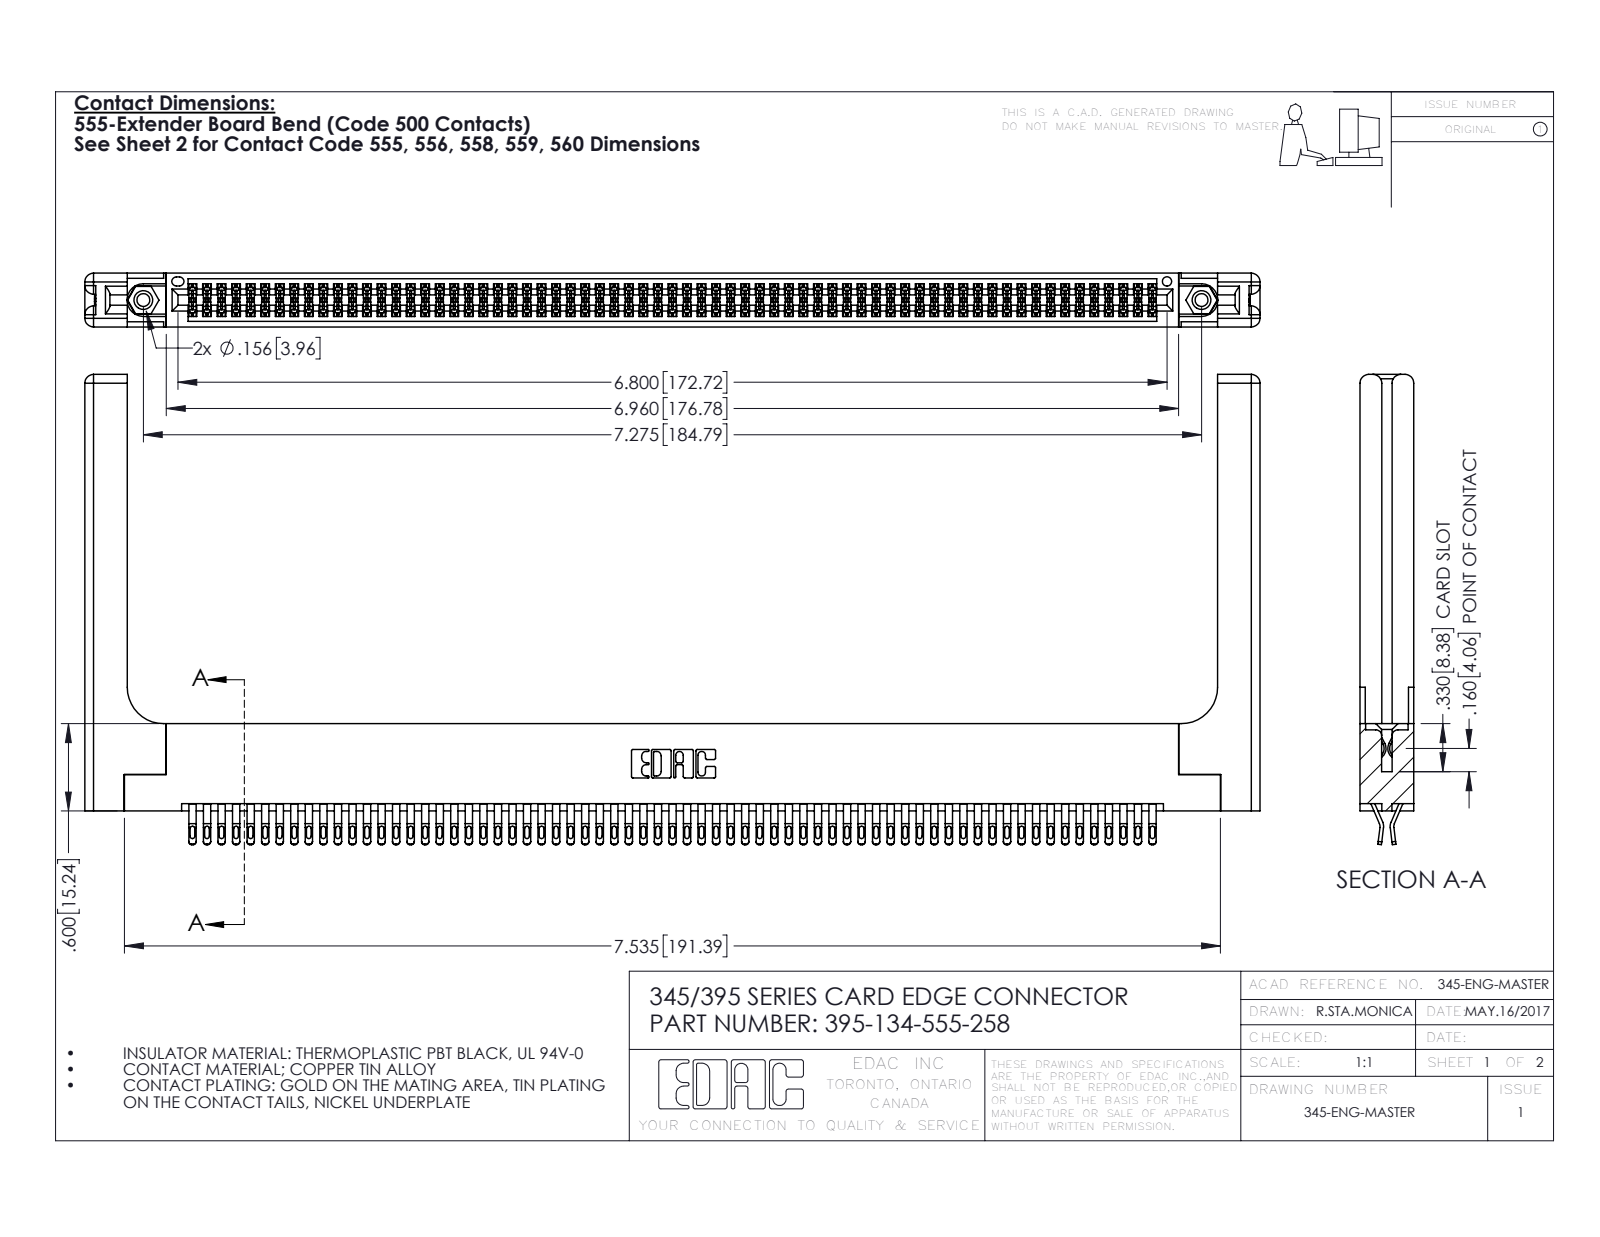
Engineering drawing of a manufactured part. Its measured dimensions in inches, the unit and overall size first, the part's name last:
Units: inches
Overall size (bounding box): 8.079 × 3.232 × 0.37
Round holes (diameter × count): ⌀0.089 ×2, ⌀0.125 ×2, ⌀0.156 ×2, ⌀0.064 ×1
Round bosses / shafts (diameter × count): ⌀0.155 ×2
Partial cylindrical surfaces — rounded edges, fillets, slot ends (radius × count): R0.016 ×335, R0.02 ×268, R0.006 ×201, R0.01 ×22, R0.06 ×16, R0.007 ×6, R0.031 ×6, R0.026 ×3
Main face-to-face distances: 0.072, 0.298, 0.37, 0.025, 0.2, 0.098, 0.272, 0.225, 0.148, 0.15
Hole centre spacings: 0.27, 7.039, 7.275
Volume: 1.772 in³ · Surface area: 57.78 in²
Bodies: 139 solids, 7886 faces (4382 planar, 3444 cylindrical, 60 other)
Part name (STEP PRODUCT): 345-292-001_555 Tail; 345-220-058_345-220-058; 395-134-555-258; 345-250-001_345-250-001-102 (+1 more)
STEP written by: SolidWorks 2016 (CONFIG_CONTROL_DESIGN)
